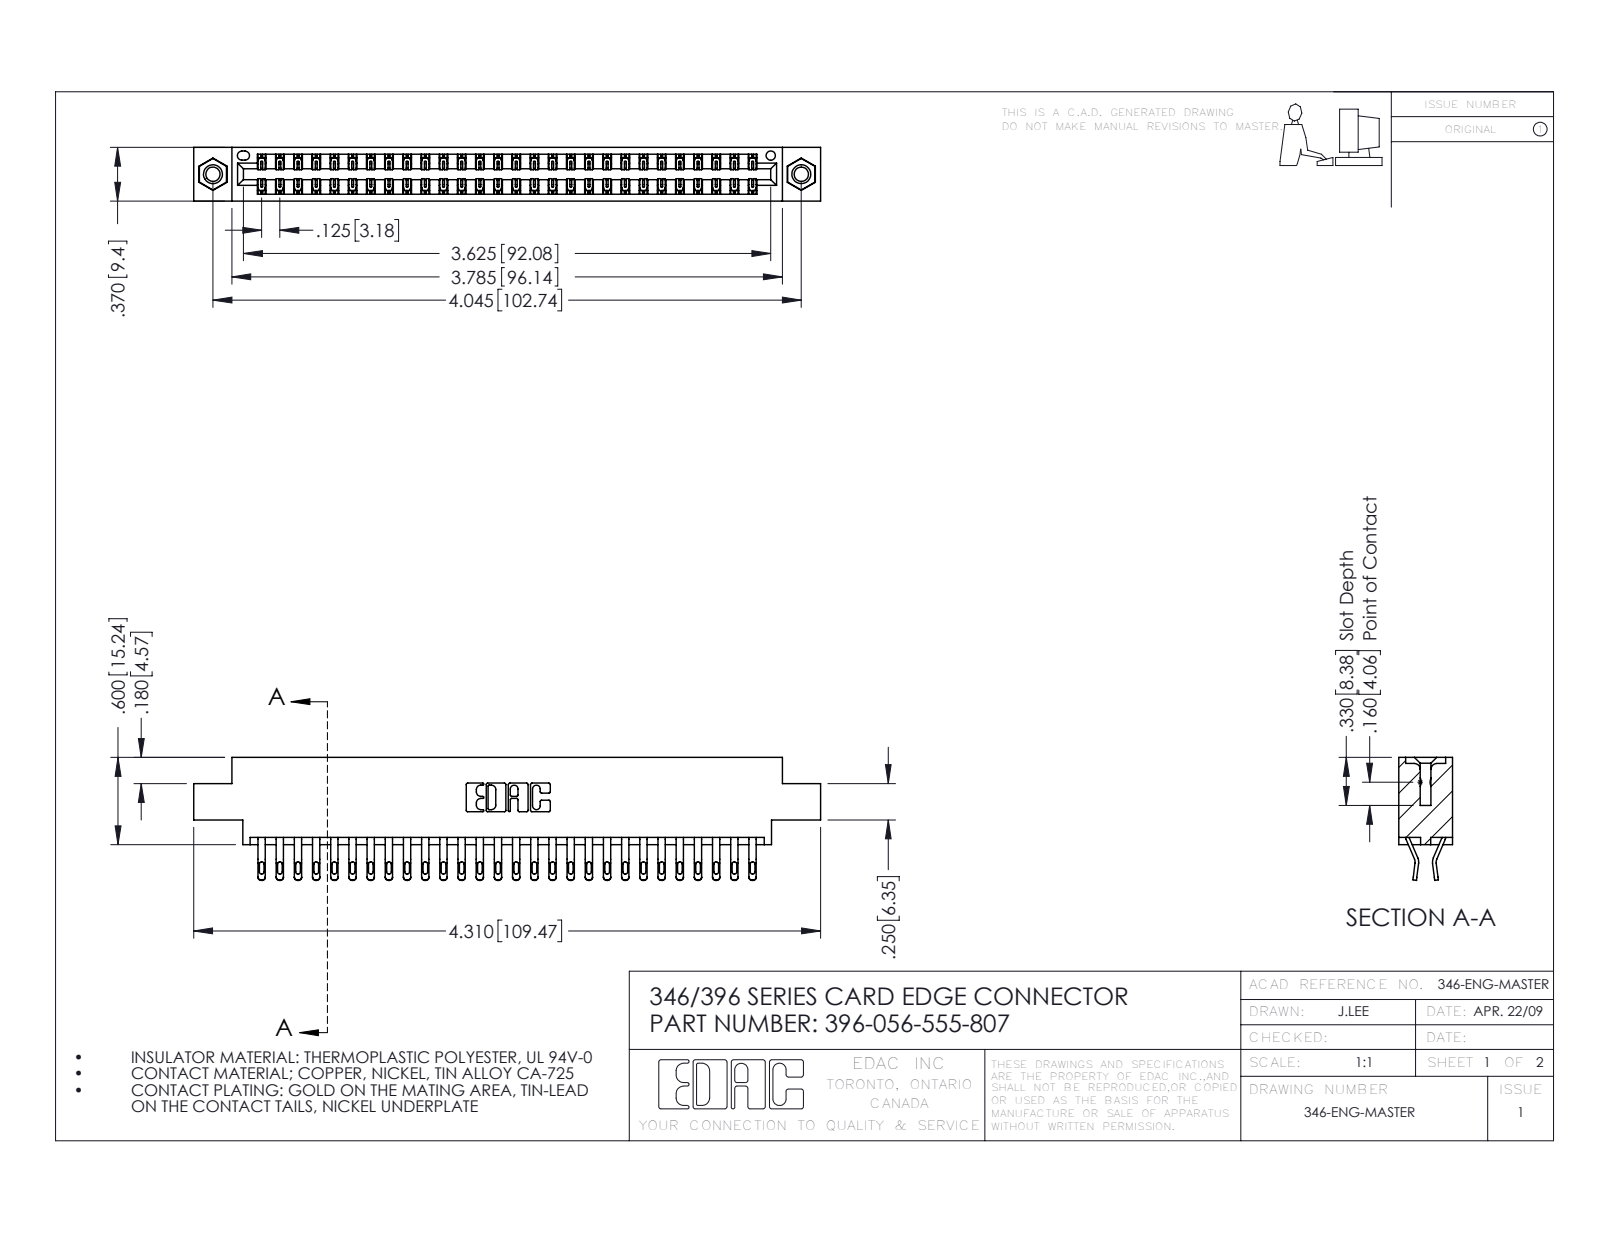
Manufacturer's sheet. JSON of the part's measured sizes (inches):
{"part_name": "396-056-555-807; 346 Part_0.170 Offset - 0.156 Dia-TI; 345-292-001_555 Tail; 345-250-001_345-250-005-103", "step_written_by": "SolidWorks 2016 (CONFIG_CONTROL_DESIGN)", "units": "inches", "bodies": {"solids": 59, "faces": 3434, "planar": 1960, "cylindrical": 1458, "other": 16}, "overall_size": [4.31, 0.845, 0.37], "volume_in3": 0.644, "surface_area_in2": 23.39, "round_holes": [[0.098, 2], [0.125, 2], [0.156, 2], [0.064, 1]], "round_bosses_or_shafts": [[0.155, 2]], "partial_cylinders_radius": [[0.016, 112], [0.02, 112], [0.006, 84], [0.01, 22], [0.007, 6], [0.031, 6], [0.026, 3], [0.01, 2]], "face_to_face_distances": [0.048, 0.322, 0.37, 0.25, 0.025, 0.072, 0.298, 0.275, 0.222, 0.148], "hole_center_spacings": [0.246, 3.837, 4.045]}
